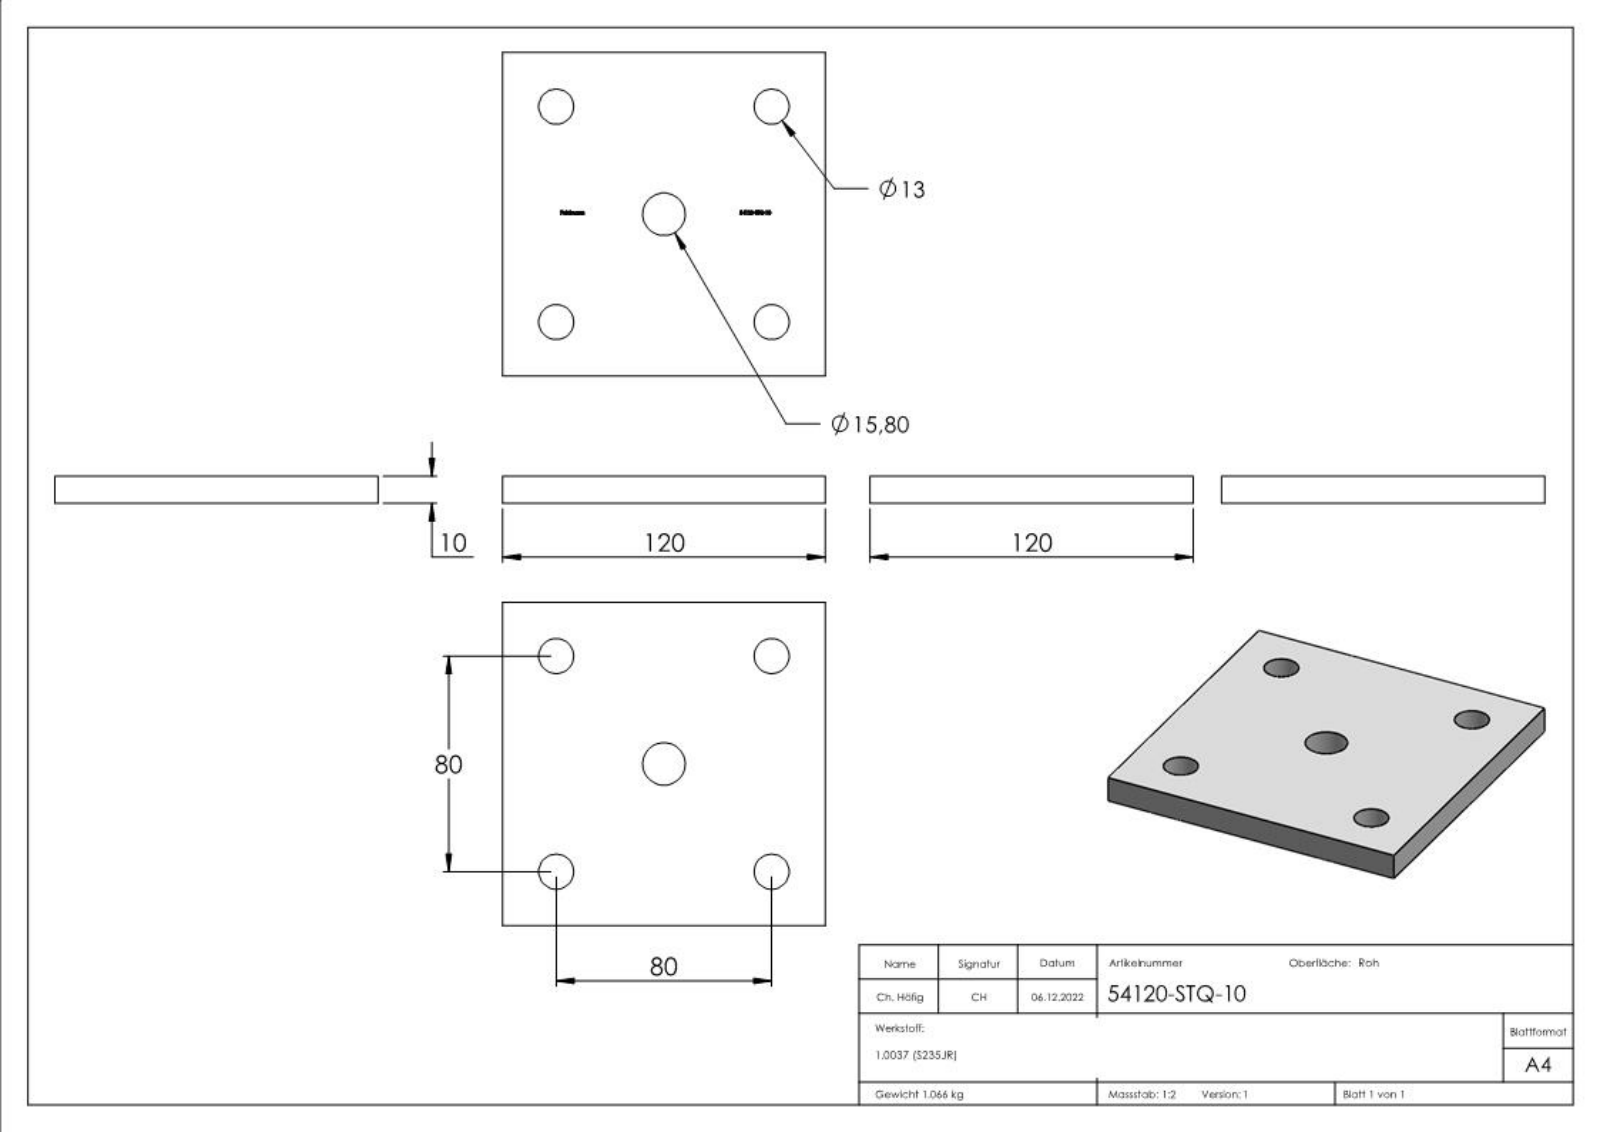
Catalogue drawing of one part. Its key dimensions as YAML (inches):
part_name: "54120-STQ-10"
step_written_by: "SolidWorks 2018 (CONFIG_CONTROL_DESIGN)"
units: inches
bodies: {solids: 1, faces: 258, planar: 148, cylindrical: 5, other: 105}
overall_size: [4.724, 4.724, 0.394]
volume: 8.344
surface_area: 53.14
round_holes:
  - {diameter: 0.512, count: 4}
  - {diameter: 0.622, count: 1}
face_to_face_distances: [0.394, 4.724, 0.39, 2.362, 0.017, 2.38, 0.296, 0.035, 0.174, 0.122]
hole_center_spacings: [2.227, 3.15, 4.454]
